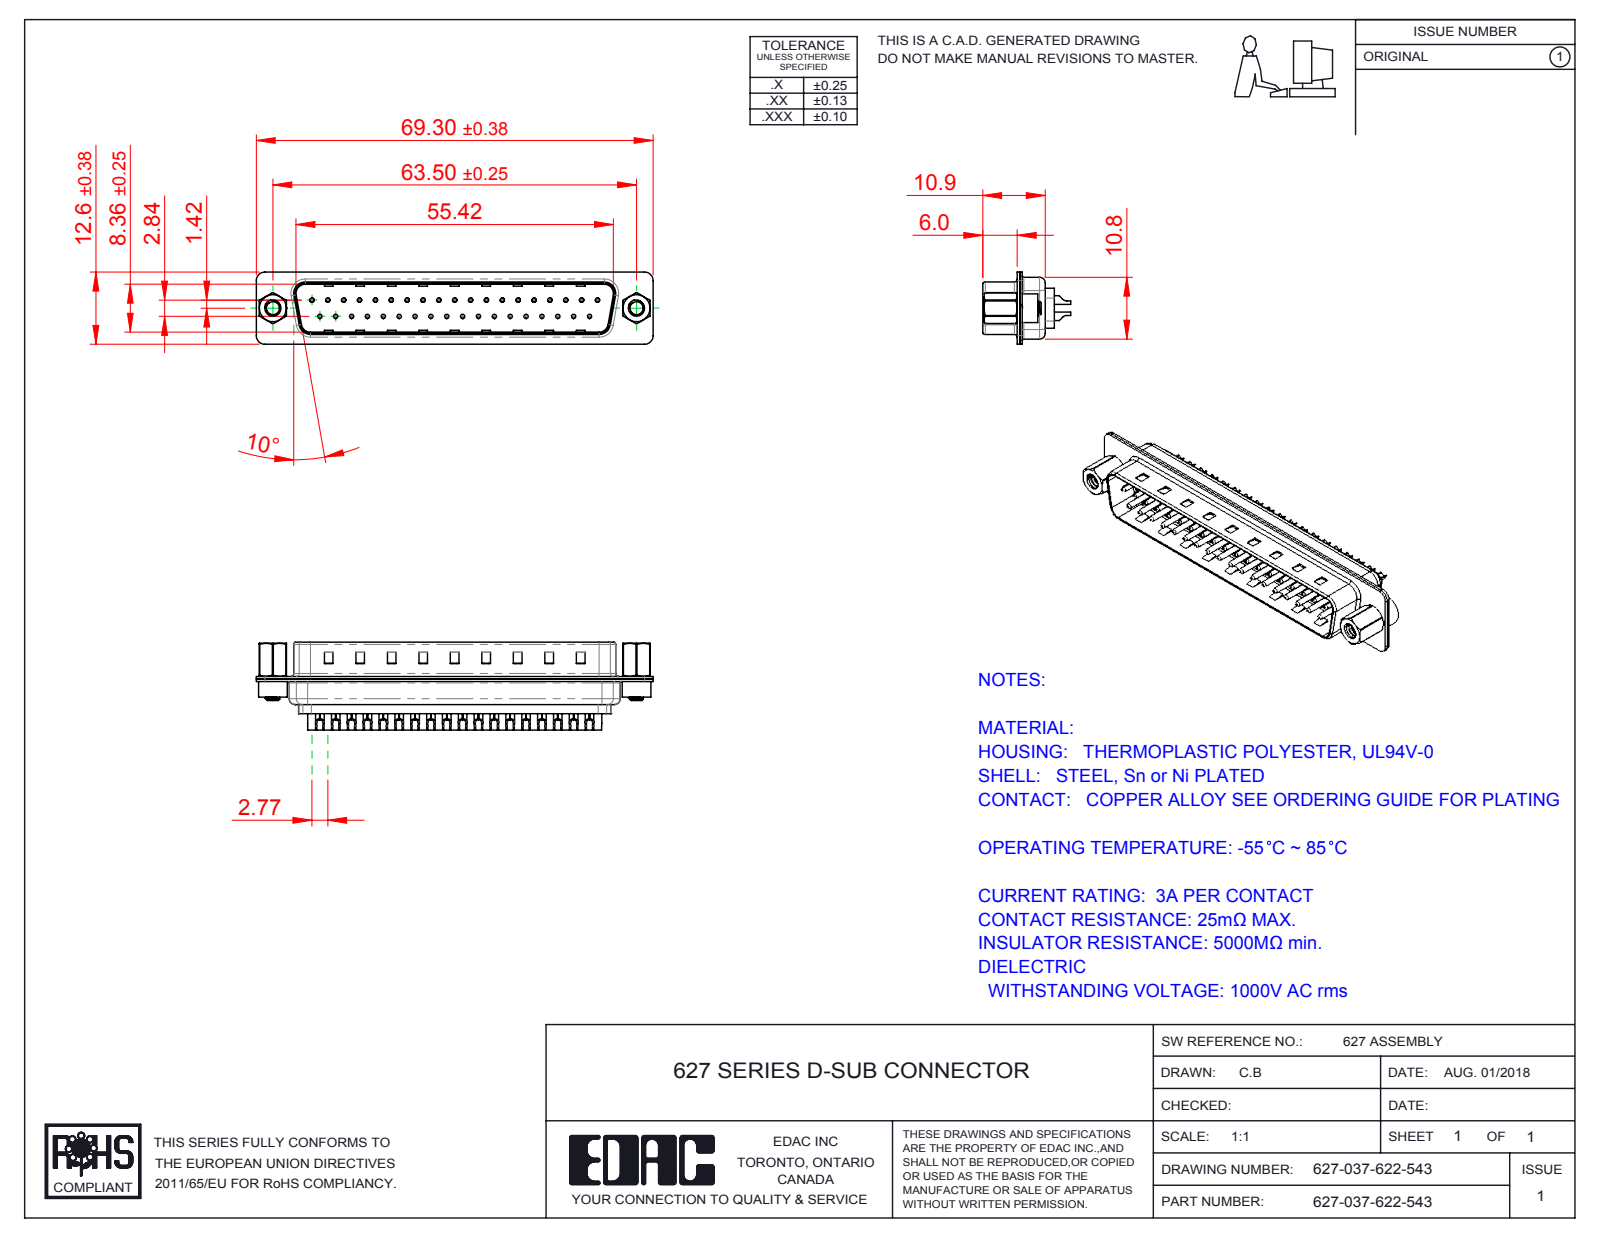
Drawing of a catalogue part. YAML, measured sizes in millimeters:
part_name: "627 4-40 Threaded Rivet; 627 4-40 Hex Standoff; 627-037-622-543; 627 Housing_37 LP (+4 more)"
step_written_by: "SolidWorks 2016 (CONFIG_CONTROL_DESIGN)"
units: millimeters
bodies: {solids: 44, faces: 2906, planar: 743, cylindrical: 1286, other: 877}
overall_size: [69.3, 15.35, 12.6]
volume: 3929
surface_area: 11246
round_holes:
  - {diameter: 0.35, count: 37}
  - {diameter: 1.1, count: 37}
  - {diameter: 1.6, count: 37}
  - {diameter: 2.26, count: 2}
  - {diameter: 2.29, count: 2}
  - {diameter: 4, count: 2}
  - {diameter: 4.8, count: 2}
round_bosses_or_shafts:
  - {diameter: 2, count: 37}
  - {diameter: 1.5, count: 37}
  - {diameter: 0.75, count: 37}
  - {diameter: 5, count: 2}
  - {diameter: 4.9, count: 2}
  - {diameter: 2.79, count: 2}
partial_cylinders:
  - {radius: 1.5, count: 16}
  - {radius: 2, count: 12}
  - {radius: 0.5, count: 8}
  - {radius: 1.6, count: 8}
  - {radius: 1, count: 6}
  - {radius: 0.25, count: 4}
  - {radius: 0.6, count: 4}
  - {radius: 0.65, count: 4}
face_to_face_distances: [0.4, 0.82, 9.58, 0.45, 8.76, 0.9, 1.5, 1.4, 6.05, 6.5]
hole_center_spacings: [3.16, 2.77, 5.54, 8.31, 5.04, 10.1, 11.08, 12.78]
